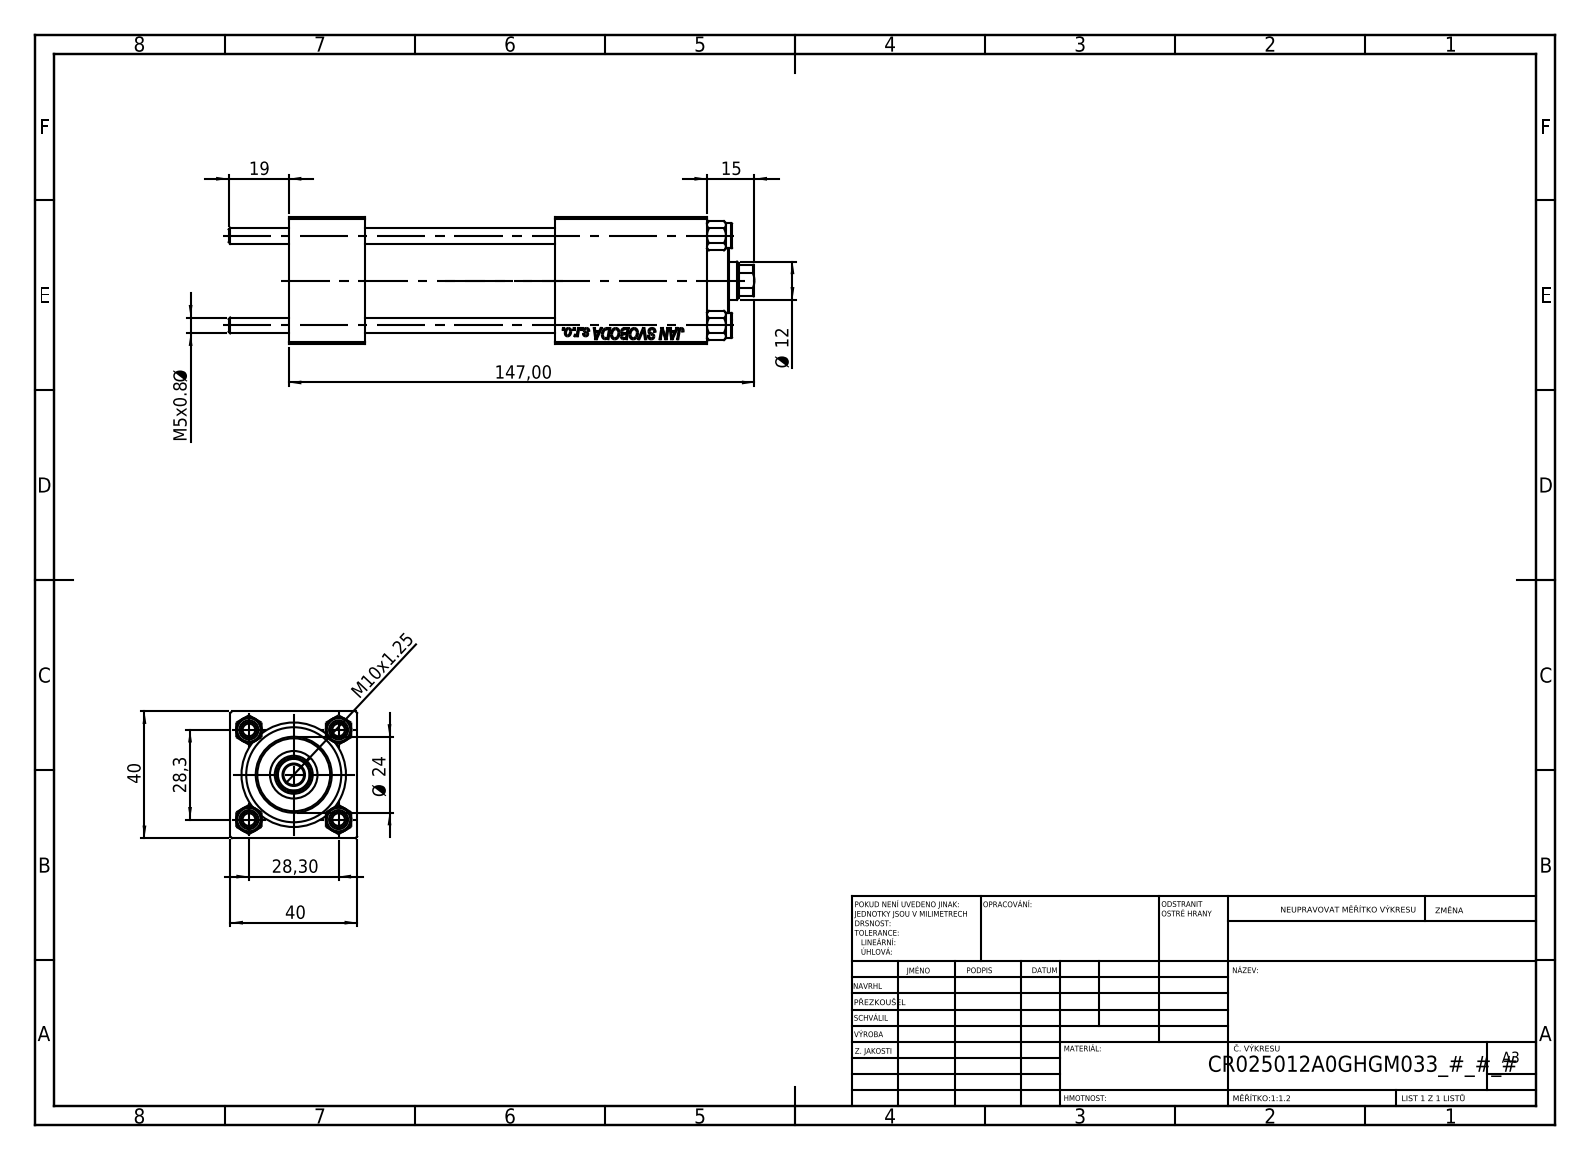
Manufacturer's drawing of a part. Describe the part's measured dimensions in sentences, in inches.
The part is named "V215_VC_A; CR025_012_A_0_G_A_G_M_020_+#_##_TYCINKA; V215CR_BODY_A; NUT_M5 (+1 more)". Its 3-D file was written by "SolidWorks 2019 (CONFIG_CONTROL_DESIGN)". It is 11 solids with 1131 faces: 517 planar, 78 cylindrical and 536 other. Overall it measures 6.535 by 1.575 by 1.575 inches. Its volume is 9.199 cubic inches and its surface area 96.82 square inches. Round holes: 4 of diameter 0.197, 3 of diameter 0.787, 2 of diameter 0.276, 2 of diameter 0.518, 1 of diameter 0.256, 1 of diameter 0.472, 1 of diameter 0.591, 1 of diameter 0.984, 1 of diameter 1.181. Round bosses or shafts: 4 of diameter 0.315, 1 of diameter 1.22, 1 of diameter 0.945. Partial cylindrical surfaces (rounded edges, fillets, slot ends): 1 of radius 0.217. The main face-to-face distances are 1.575, 0.945, 5.197, 4.252, 4.067, 3.122, 1.13, 3.307, 2.362, 0.76. The hole center spacings are 0.788, 1.114, 1.576, 3.346.
